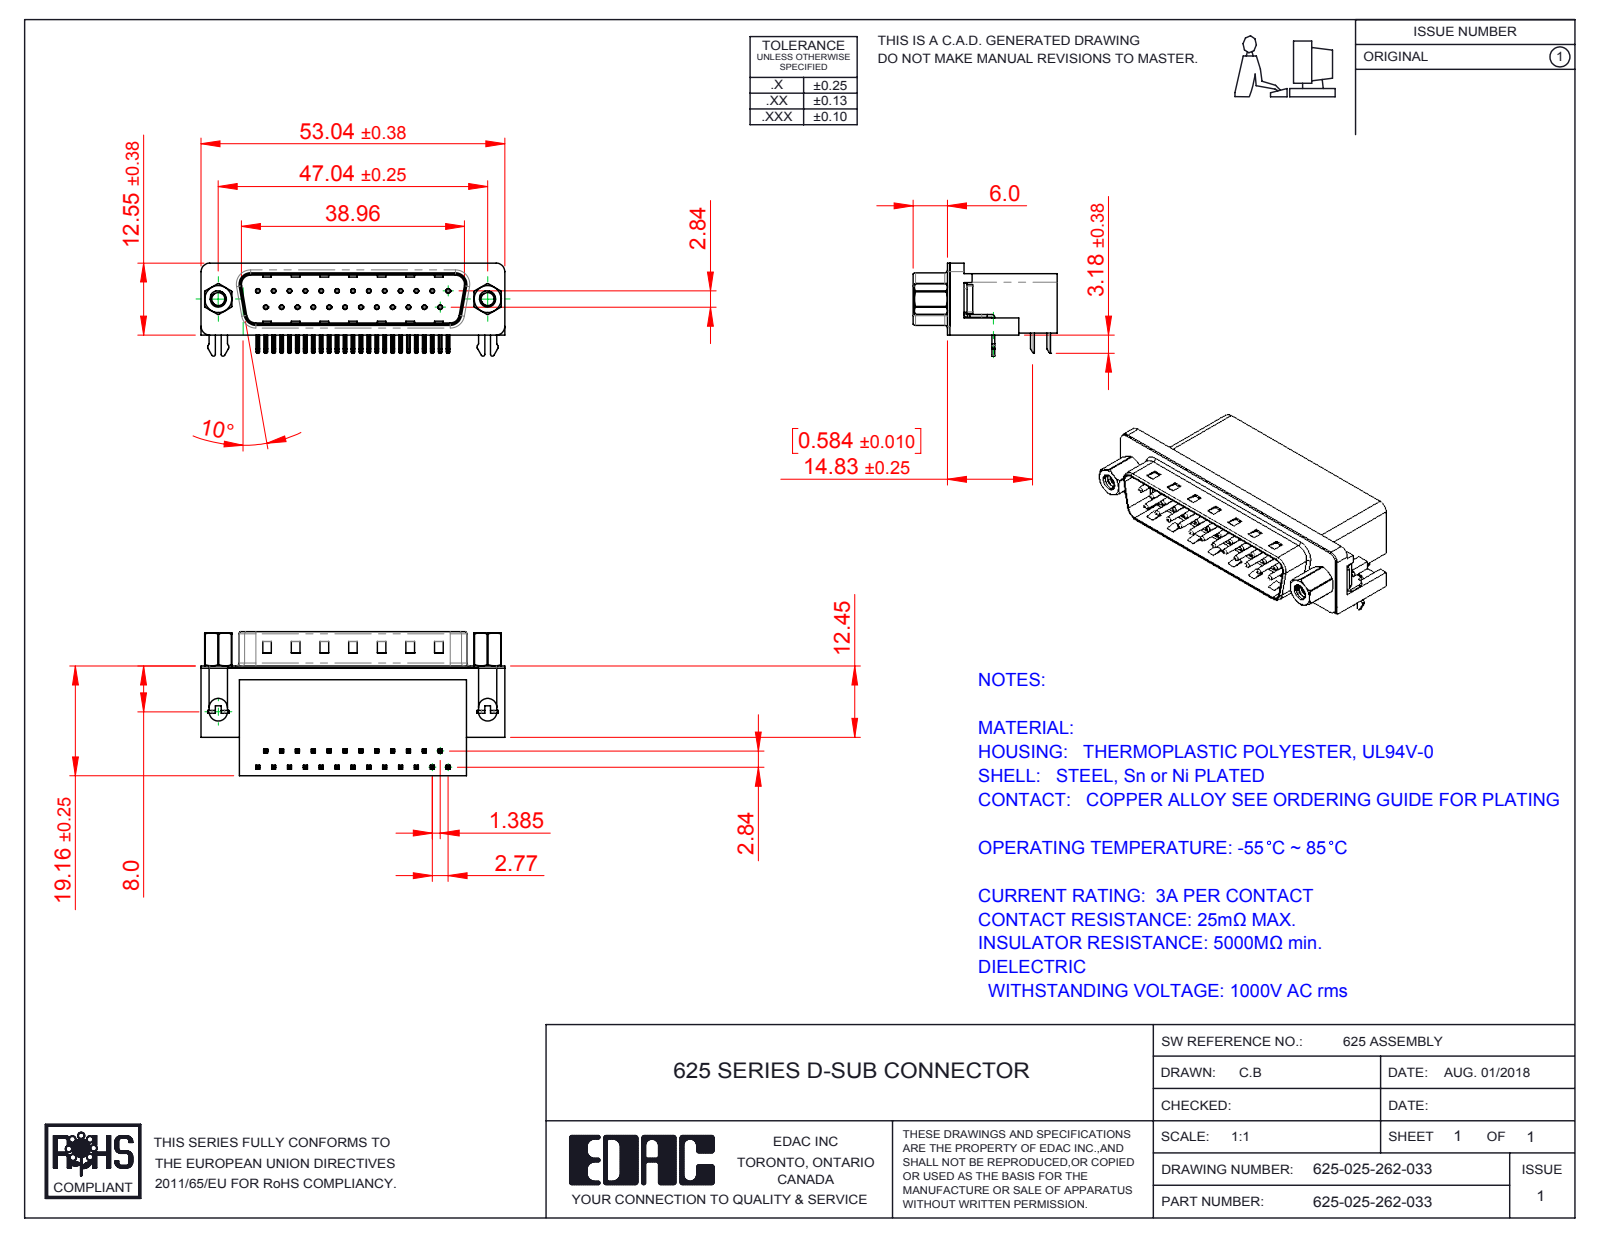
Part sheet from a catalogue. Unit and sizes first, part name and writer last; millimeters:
Units: millimetres
Overall size (bounding box): 53.04 × 25.16 × 16.25
Round holes (diameter × count): ⌀0.35 ×25, ⌀0.8 ×25, ⌀2.26 ×2, ⌀2.29 ×2, ⌀4 ×2, ⌀4.8 ×2, ⌀5 ×2
Round bosses / shafts (diameter × count): ⌀0.75 ×25, ⌀4.9 ×2, ⌀4.75 ×2, ⌀3.9 ×2, ⌀2.79 ×2
Partial cylindrical surfaces — rounded edges, fillets, slot ends (radius × count): R0.25 ×108, R0.12 ×50, R1 ×16, R0.5 ×14, R1.6 ×8, R1.5 ×7, R0.32 ×4, R0.9 ×4
Main face-to-face distances: 0.4, 10.35, 18.76, 2.1, 8.76, 10.46, 10.86, 1.7, 19.16, 10.11
Hole centre spacings: 3.16, 2.77, 11.08, 5.54, 8.31, 5.03, 13.85, 7.48
Volume: 9 377 mm³ · Surface area: 9 350 mm²
Bodies: 33 solids, 2431 faces (1459 planar, 741 cylindrical, 231 other)
Part name (STEP PRODUCT): 625 Contact Bottom; 625-025-262-033; 625 4-40 Threaded Rivet; 625 Housing_25 Socket (+4 more)
STEP written by: SolidWorks 2016 (CONFIG_CONTROL_DESIGN)
